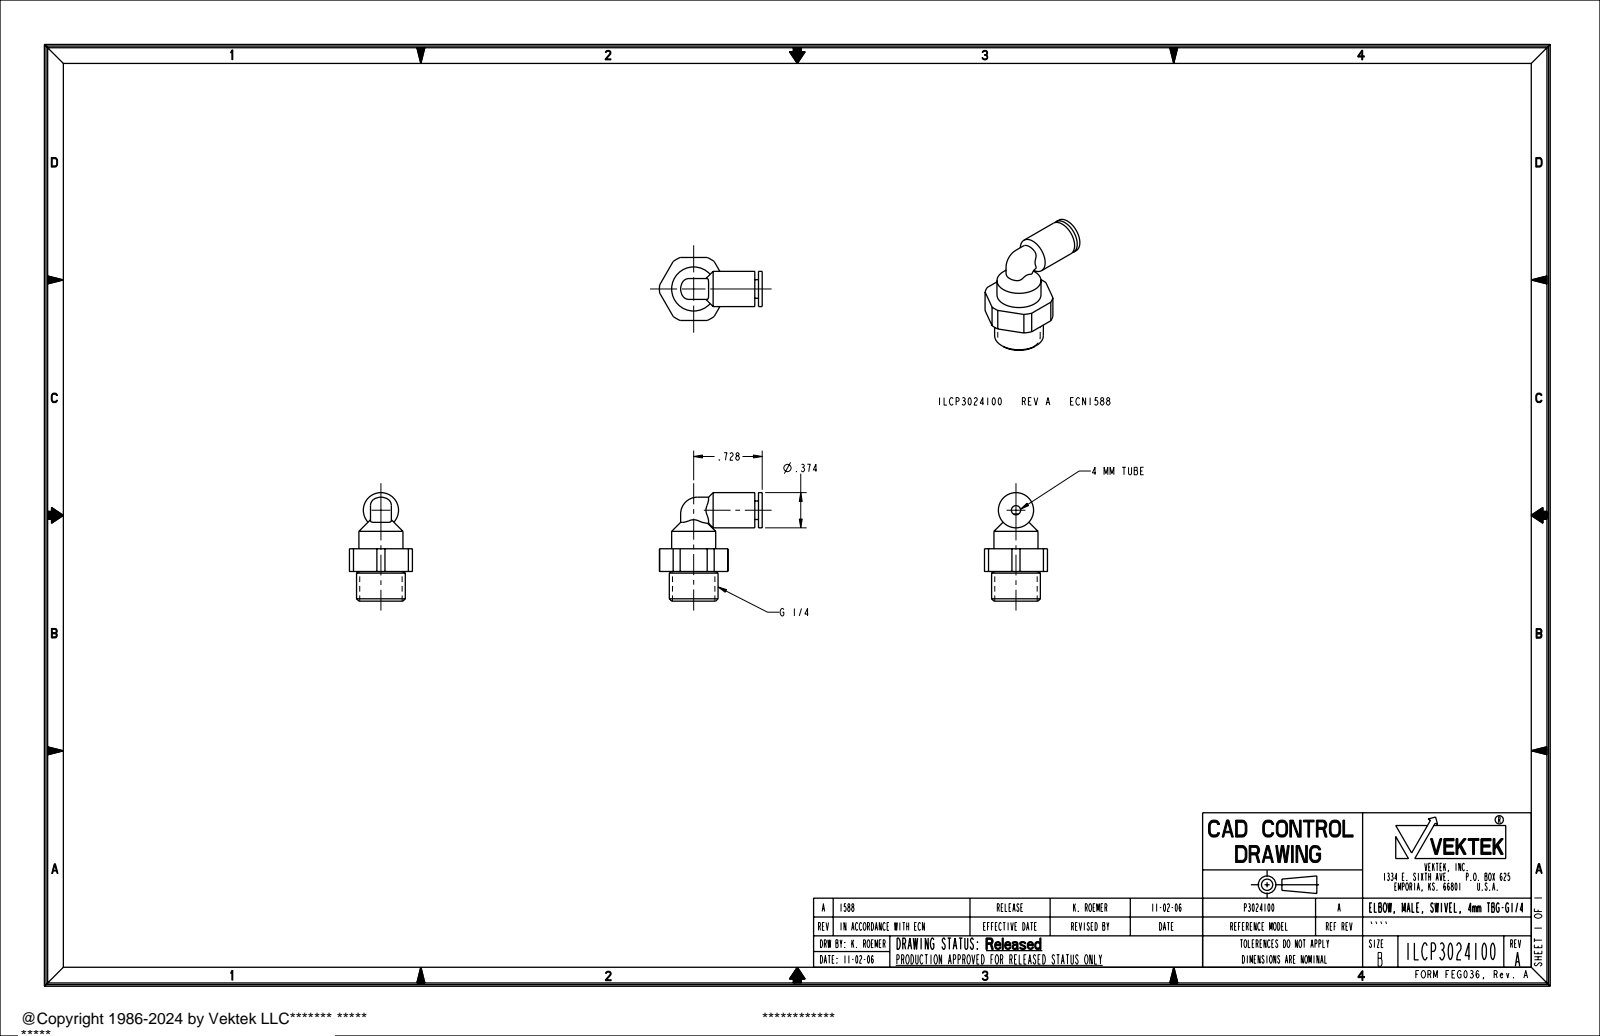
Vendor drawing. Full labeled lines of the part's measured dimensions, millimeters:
Part name (STEP PRODUCT): ILCP3024100
STEP written by: PRO/ENGINEER BY PARAMETRIC TECHNOLOGY CORPORATION, 2005180 (AUTOMOTIVE_DESIGN_CC2)
Units: millimetres
Bodies: 1 solid, 61 faces (15 planar, 30 cylindrical, 16 other)
Overall size (bounding box): 29.3 × 27.7 × 17
Volume: 4 280 mm³ · Surface area: 2 703 mm²
Round holes (diameter × count): ⌀2.5 ×2
Round bosses / shafts (diameter × count): ⌀13.2 ×1, ⌀11.9 ×1, ⌀11.5 ×1, ⌀9.5 ×1, ⌀5 ×1
Partial cylindrical surfaces — rounded edges, fillets, slot ends (radius × count): R2 ×4, R3.5 ×2, R9.2 ×1
Main face-to-face distances: 6.1, 17, 8, 14.1, 1, 2, 5.7, 11.3, 5.6, 18.5
